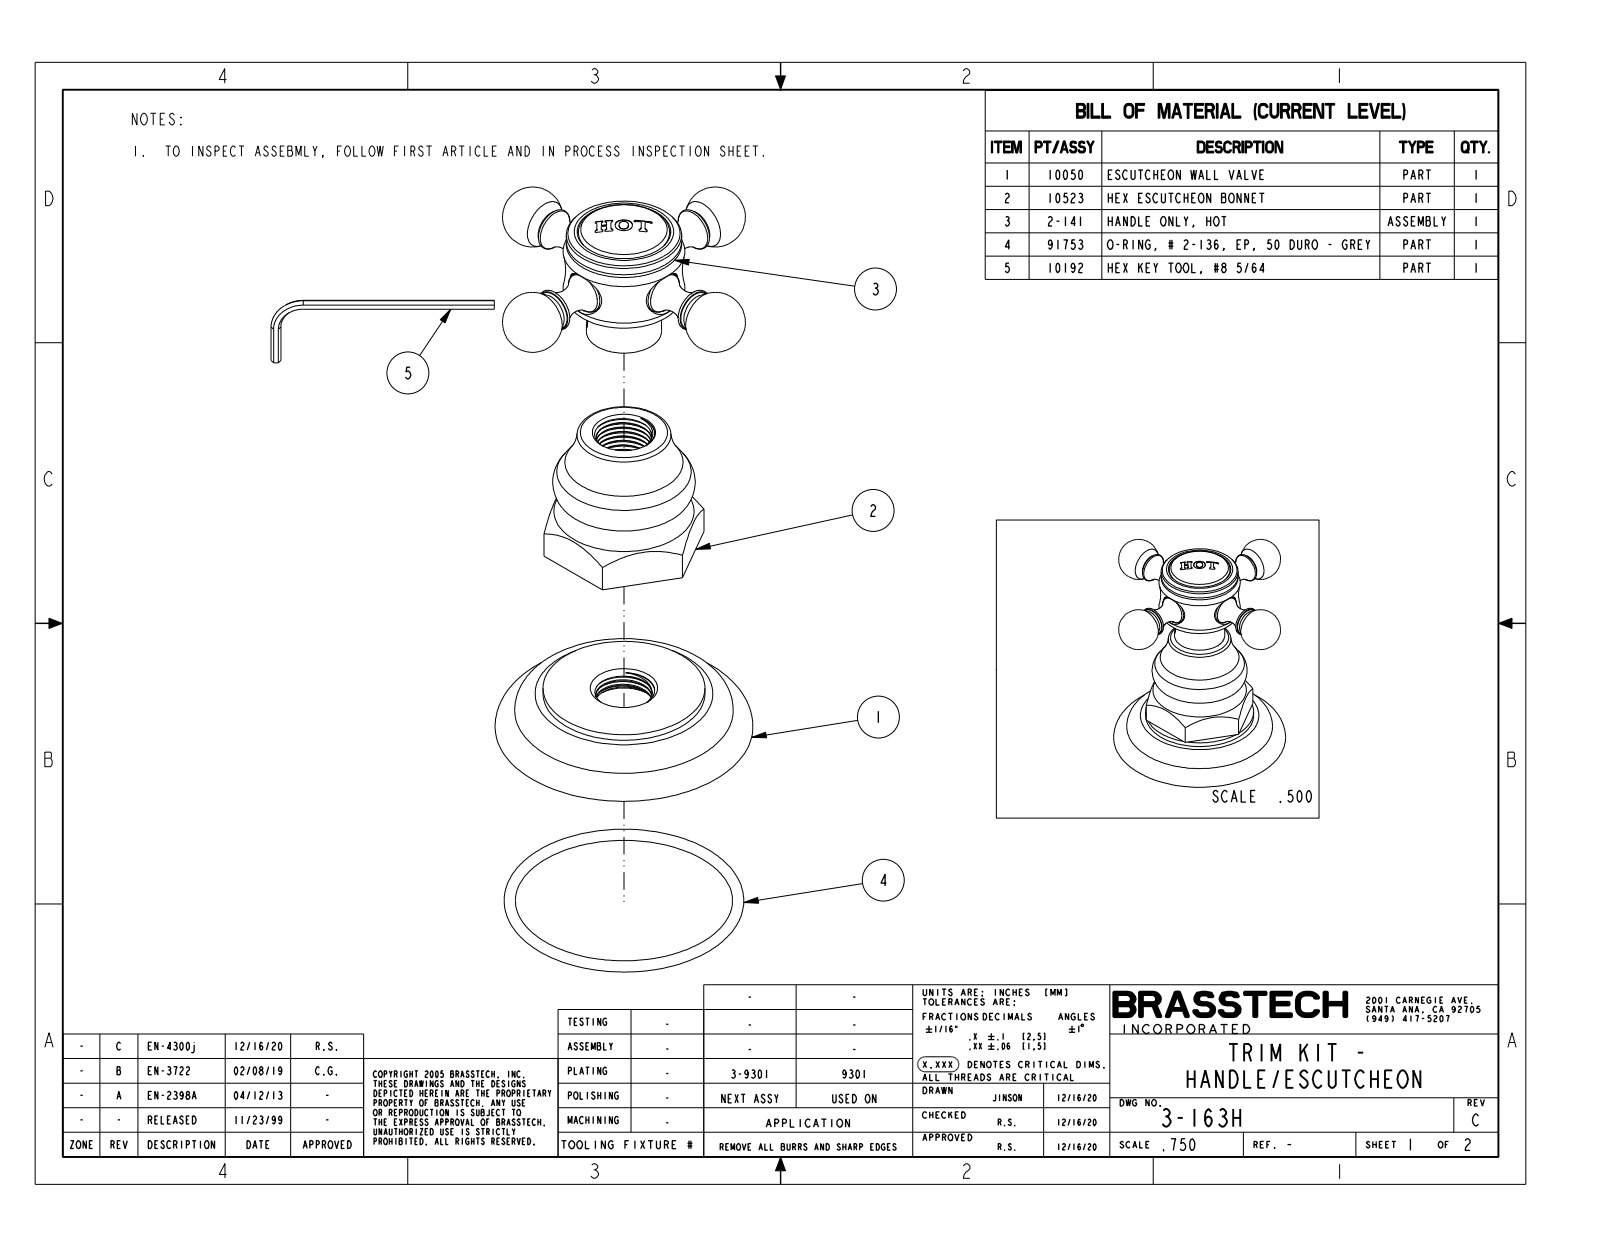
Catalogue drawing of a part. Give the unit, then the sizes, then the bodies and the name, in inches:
Units: inches
Overall size (bounding box): 2.915 × 2.915 × 2.912
Round holes (diameter × count): ⌀0.41 ×2
Round bosses / shafts (diameter × count): ⌀0.392 ×2, ⌀1.482 ×1, ⌀1.055 ×1, ⌀0.687 ×1, ⌀0.4 ×1
Partial cylindrical surfaces — rounded edges, fillets, slot ends (radius × count): R0.024 ×7, R0.006 ×4, R0.036 ×2, R0.041 ×2
Main face-to-face distances: 1.313, 1.687, 0.375, 1.312, 1.717, 1.342, 0.03, 1.313, 0.437, 0.062
Volume: 4.129 in³ · Surface area: 24.67 in²
Bodies: 1 solid, 202 faces (64 planar, 42 cylindrical, 96 other)
Part name (STEP PRODUCT): 3-163H
STEP written by: CREO PARAMETRIC BY PTC INC, 2018400 (CONFIG_CONTROL_DESIGN)
